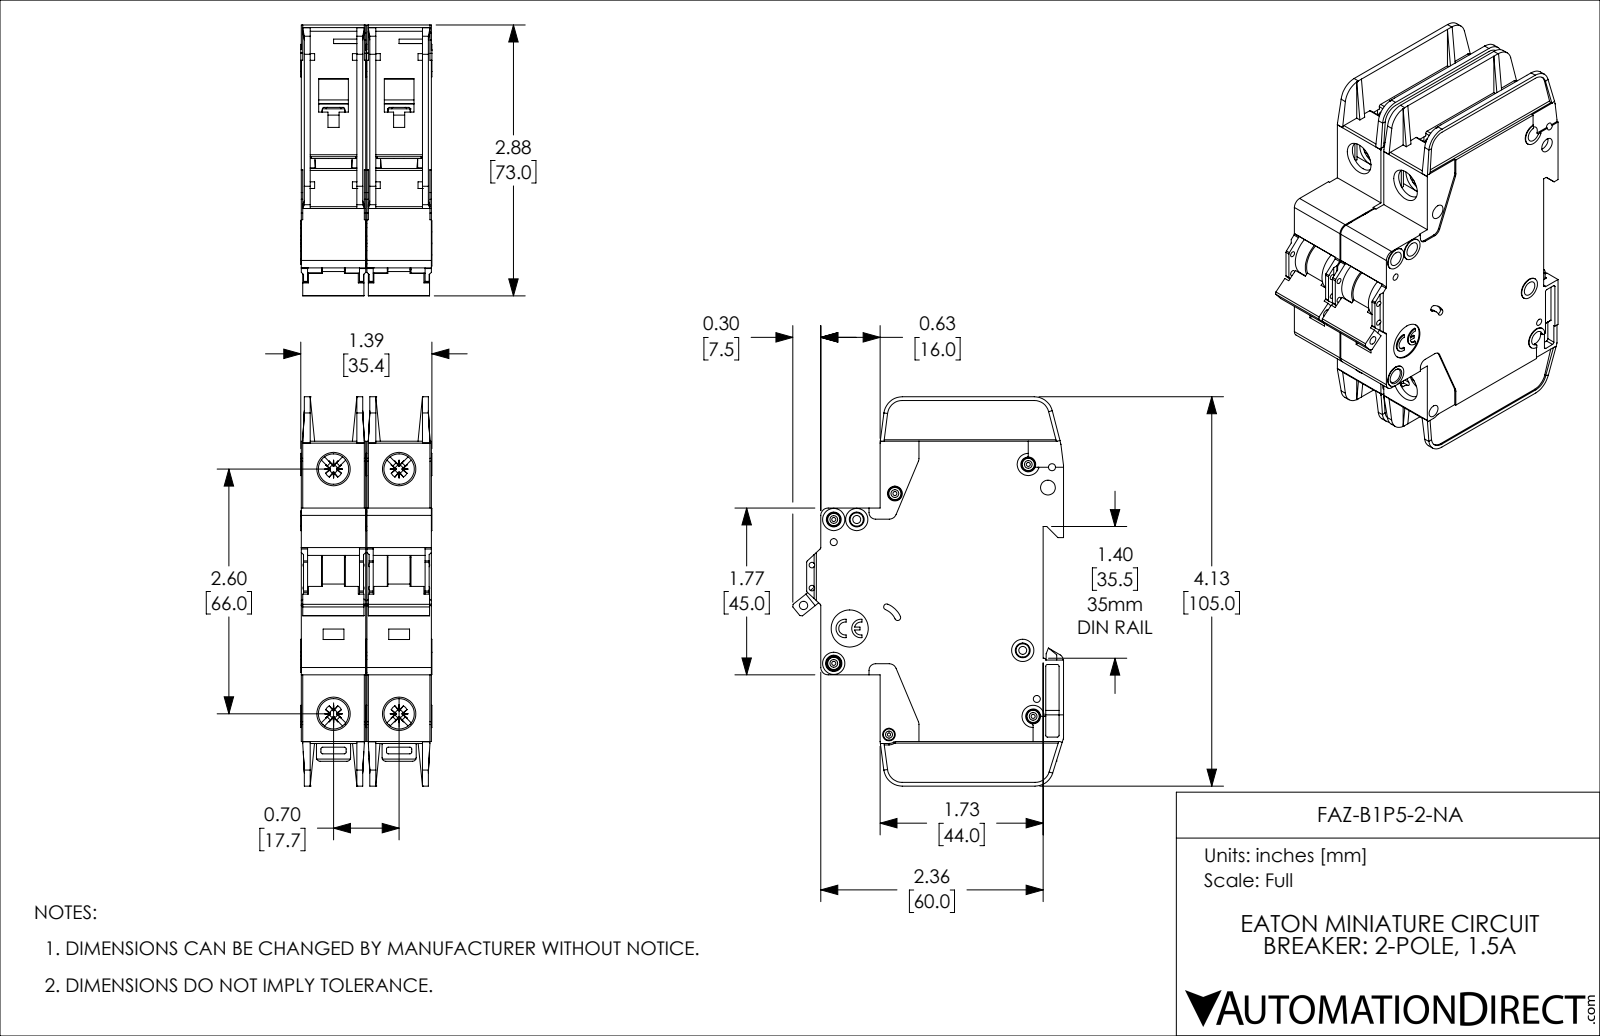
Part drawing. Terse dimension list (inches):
name: FAZ-B1P5-2-NA
written by: SolidWorks 2019 (AUTOMOTIVE_DESIGN)
unit: in
bodies: 2 solids, 2254 faces (1342 planar, 714 cylindrical, 198 other)
size: 4.134 × 2.876 × 1.394
volume: 9.365 in³; area: 82.01 in²
holes: 8× ⌀0.157, 5× ⌀0.043, 4× ⌀0.075, 4× ⌀0.323, 2× ⌀0.059, 2× ⌀0.085, 1× ⌀0.035, 1× ⌀0.089, 1× ⌀0.098, 1× ⌀0.134, 1× ⌀0.394
bosses: 5× ⌀0.13, 4× ⌀0.236, 3× ⌀0.118, 2× ⌀0.098
rounds: 57× R0.02, 20× R0.016, 14× R0.039, 10× R0.079, 8× R0.043, 5× R0.008, 5× R0.197, 4× R0.01
face distances: 0.697, 0.047, 0.685, 0.591, 0.094, 0.638, 0.543, 1.382, 0.744, 0.65
hole spacings: 0.244, 0.537, 0.697, 0.87, 2.598, 2.69, 0.189, 0.199
